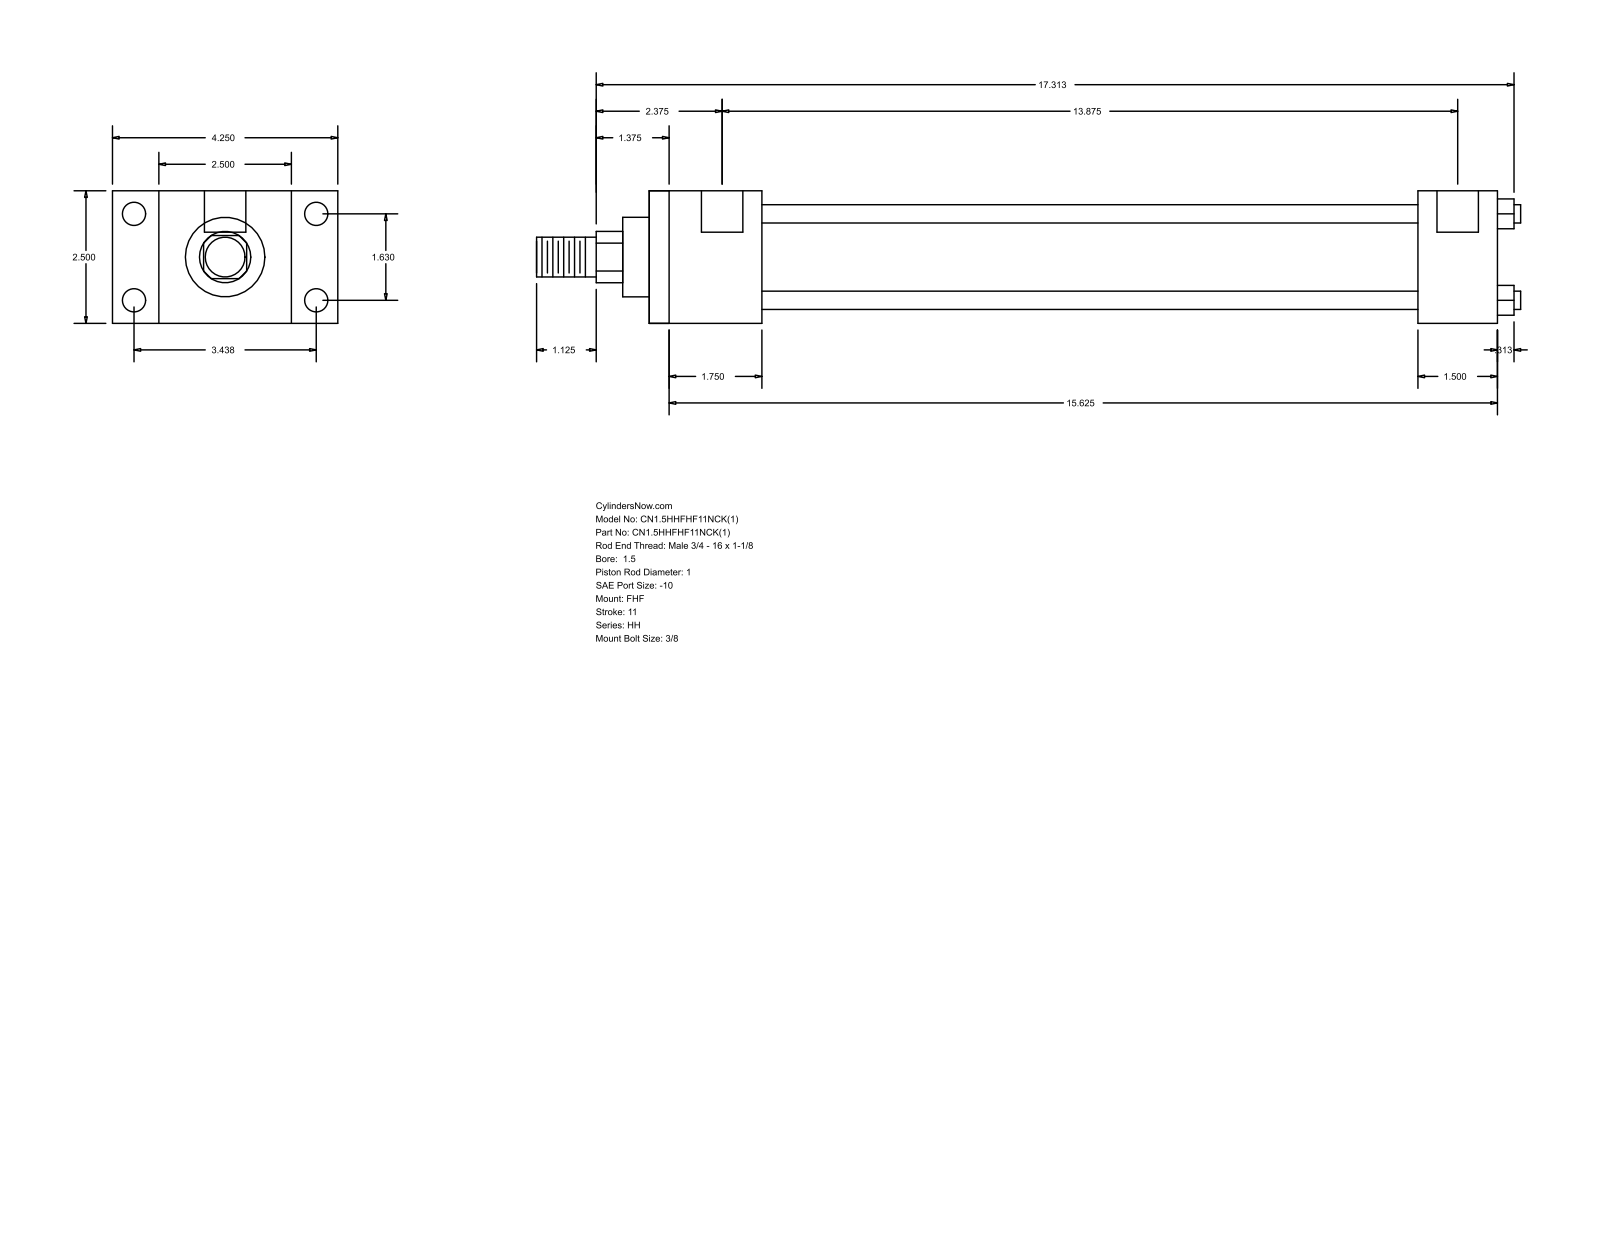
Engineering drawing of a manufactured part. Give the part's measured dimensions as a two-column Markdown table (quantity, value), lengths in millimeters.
| quantity | value |
| --- | --- |
| part name | HH_FHF__0150_1 |
| STEP written by | GSSL Pune (CONFIG_CONTROL_DESIGN) |
| units | millimeters |
| bodies | 0 solids, 88 faces (60 planar, 28 cylindrical, 0 other) |
| overall size | 471.49 × 107.95 × 63.5 |
| round holes (diameter × count) | 5.56 × 4, 11.13 × 4, 19.84 × 2 |
| round bosses / shafts (diameter × count) | 8.76 × 4, 44.45 × 1, 38.1 × 1, 25.4 × 1, 19.05 × 1 |
| partial cylindrical surfaces (radius × count) | 12.29 × 1 |
| main face-to-face distances | 63.5, 22.23, 85.73, 53.98, 107.96, 406.4, 352.42, 38.1, 368.3, 314.32 |
| hole center spacings | 1.59, 41.4, 87.32, 96.64, 354.01, 355.6, 352.42 |
